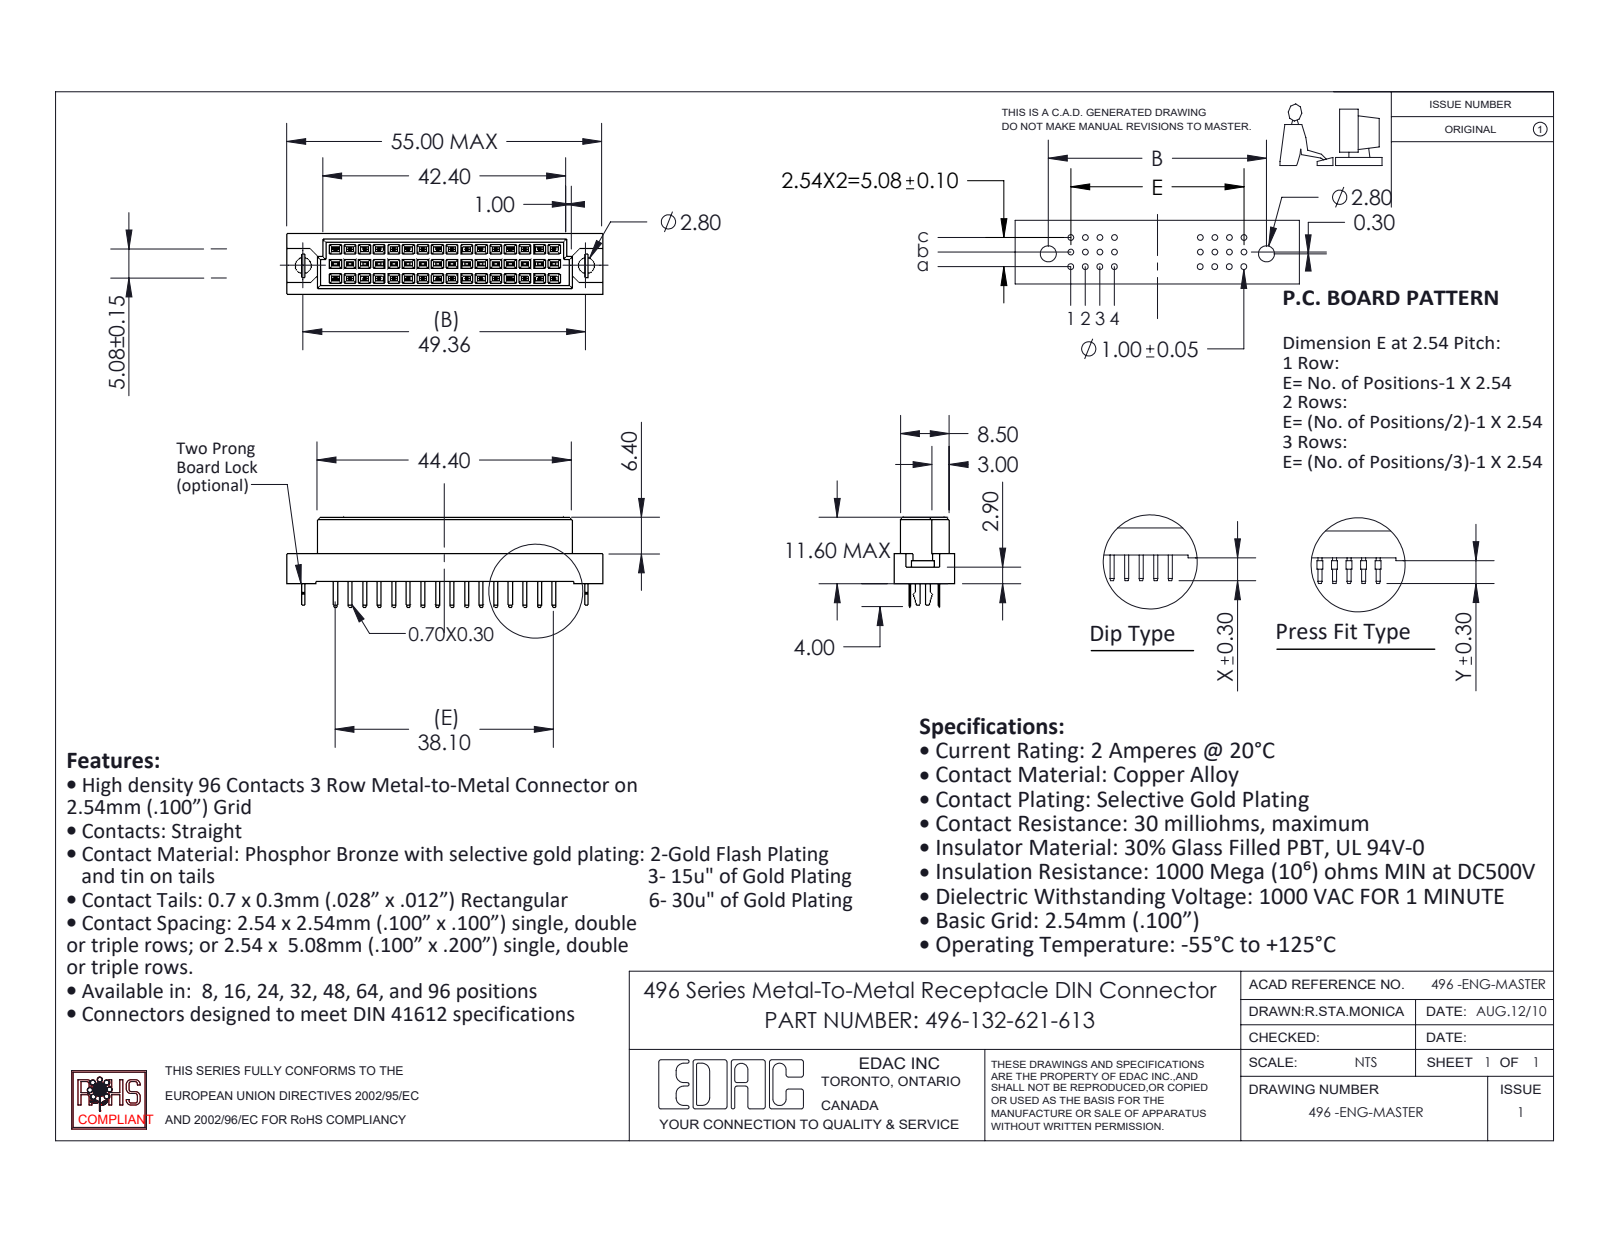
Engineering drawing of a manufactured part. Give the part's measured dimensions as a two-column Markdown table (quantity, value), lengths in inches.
| quantity | value |
| --- | --- |
| part name | 496 Part_48; 496-290_21; 496 Bore-lock; 496-132-621-613 |
| STEP written by | SolidWorks 2020 (CONFIG_CONTROL_DESIGN) |
| units | inches |
| bodies | 35 solids, 1022 faces (1016 planar, 6 cylindrical, 0 other) |
| overall size | 2.165 × 0.614 × 0.417 |
| volume | 0.285 in³ |
| surface area | 7.536 in² |
| round holes (diameter × count) | 0.11 × 2 |
| partial cylindrical surfaces (radius × count) | 0.021 × 1 |
| main face-to-face distances | 0.1, 0.2, 0.041, 0.376, 0.032, 0.022, 0.022, 0.061, 0.073, 0.103 |
| hole center spacings | 1.943 |
